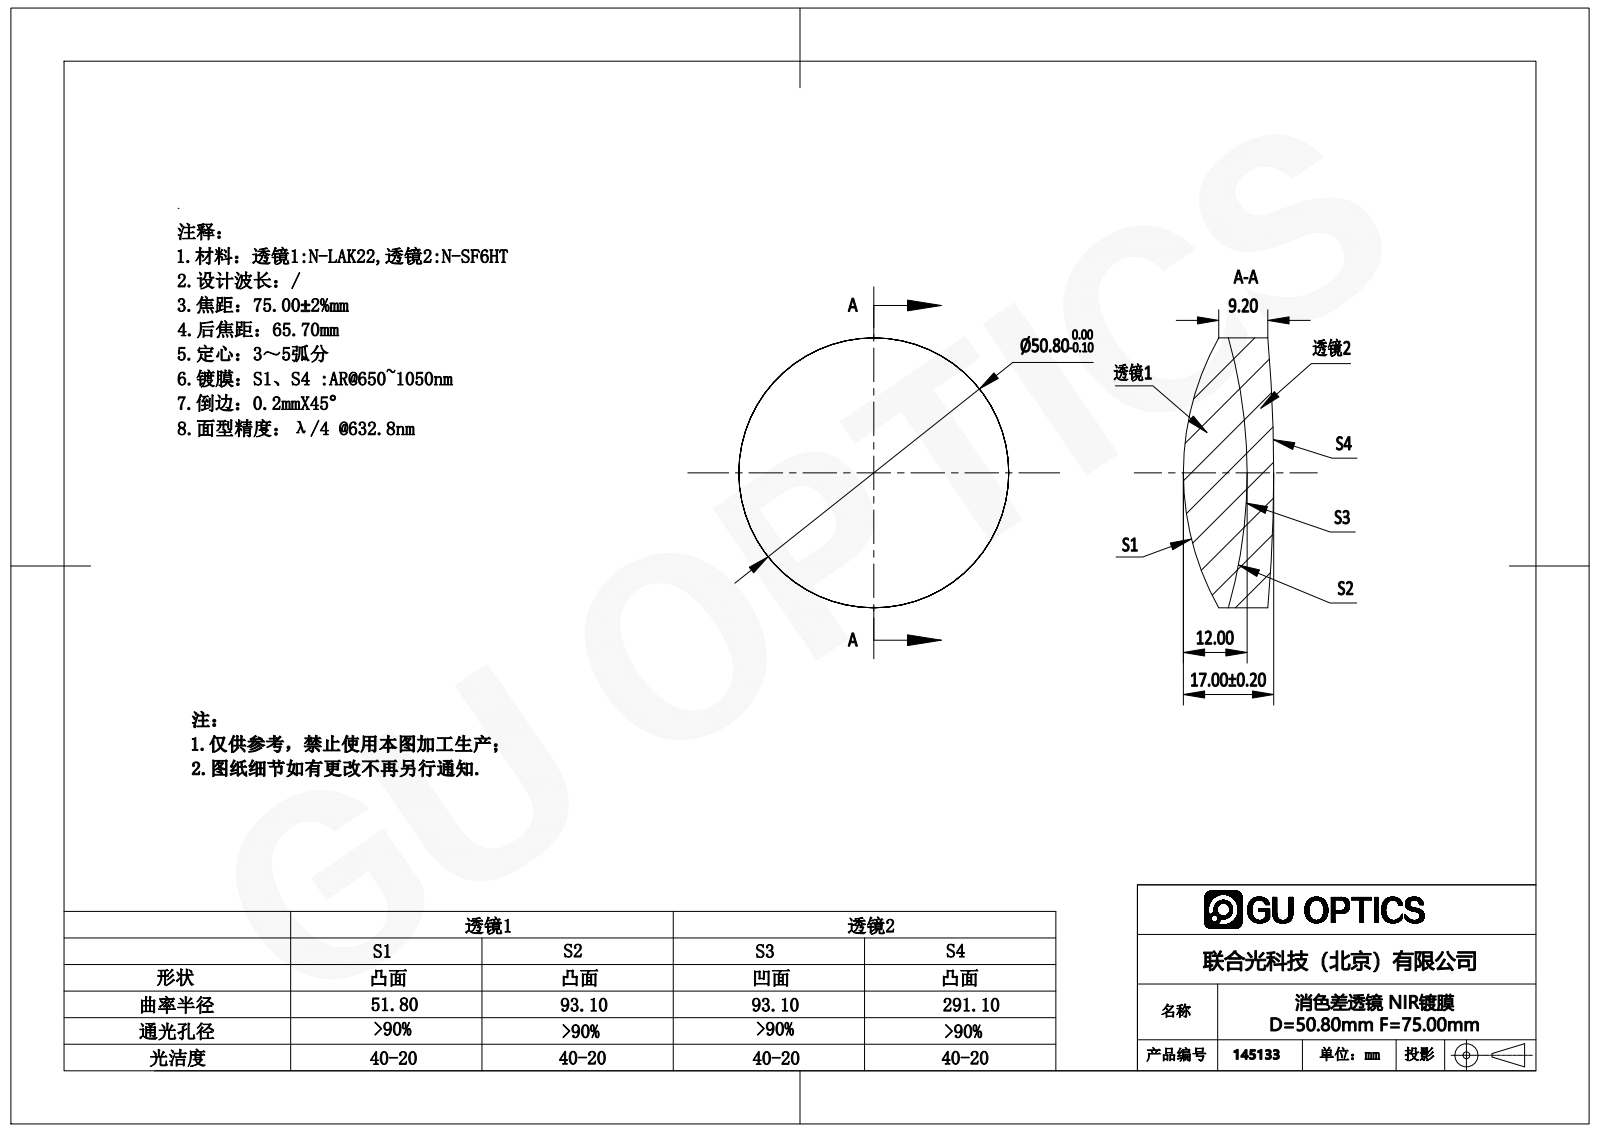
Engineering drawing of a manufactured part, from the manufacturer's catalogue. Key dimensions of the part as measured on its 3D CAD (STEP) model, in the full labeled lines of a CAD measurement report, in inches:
Part name (STEP PRODUCT): 145133
STEP written by: SolidWorks 2016 (AUTOMOTIVE_DESIGN)
Units: inches
Bodies: 2 solids, 12 faces (0 planar, 4 cylindrical, 8 other)
Overall size (bounding box): 2 × 2 × 0.669
Volume: 1.632 in³ · Surface area: 15.19 in²
Round bosses / shafts (diameter × count): ⌀2 ×1
